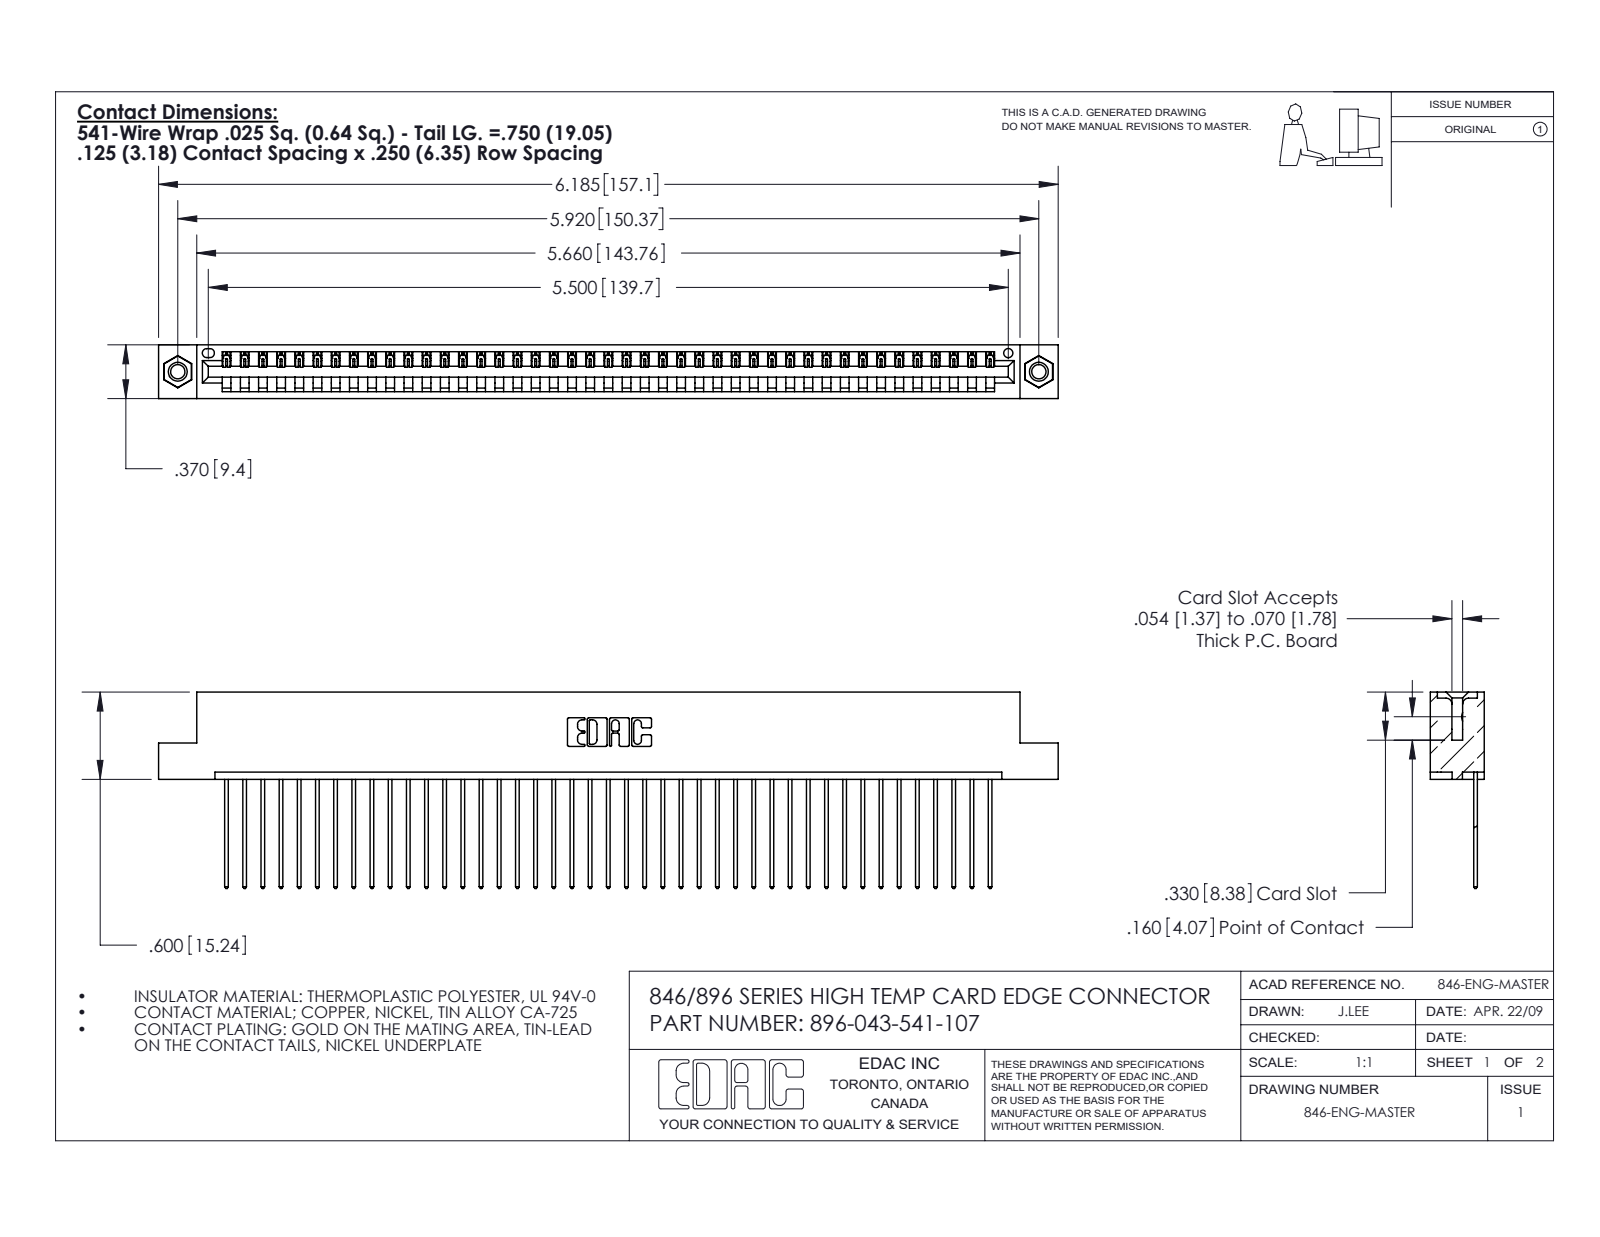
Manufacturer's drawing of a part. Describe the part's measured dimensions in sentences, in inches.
The part is named "346 Part_Flush Mounting Lugs - 0.156 Dia-TI; 345-292-001_345-293-141; 396-043-541-107; 345-250-001_345-250-005-103". Its 3-D file was written by "SolidWorks 2016 (CONFIG_CONTROL_DESIGN)". It is 46 solids with 2676 faces: 1828 planar, 832 cylindrical and 16 other. Overall it measures 6.185 by 1.35 by 0.37 inches. Its volume is 0.926 cubic inches and its surface area 30.78 square inches. Round holes: 2 of diameter 0.098, 2 of diameter 0.125, 2 of diameter 0.156, 1 of diameter 0.064. Round bosses or shafts: 2 of diameter 0.155. Partial cylindrical surfaces (rounded edges, fillets, slot ends): 86 of radius 0.006, 86 of radius 0.01, 22 of radius 0.01, 6 of radius 0.007, 6 of radius 0.031, 3 of radius 0.026, 2 of radius 0.031, 2 of radius 0.04. The main face-to-face distances are 0.048, 0.322, 0.37, 0.25, 0.072, 0.298, 0.025, 0.148, 0.222, 0.1. The hole center spacings are 0.246, 5.711, 5.92.
